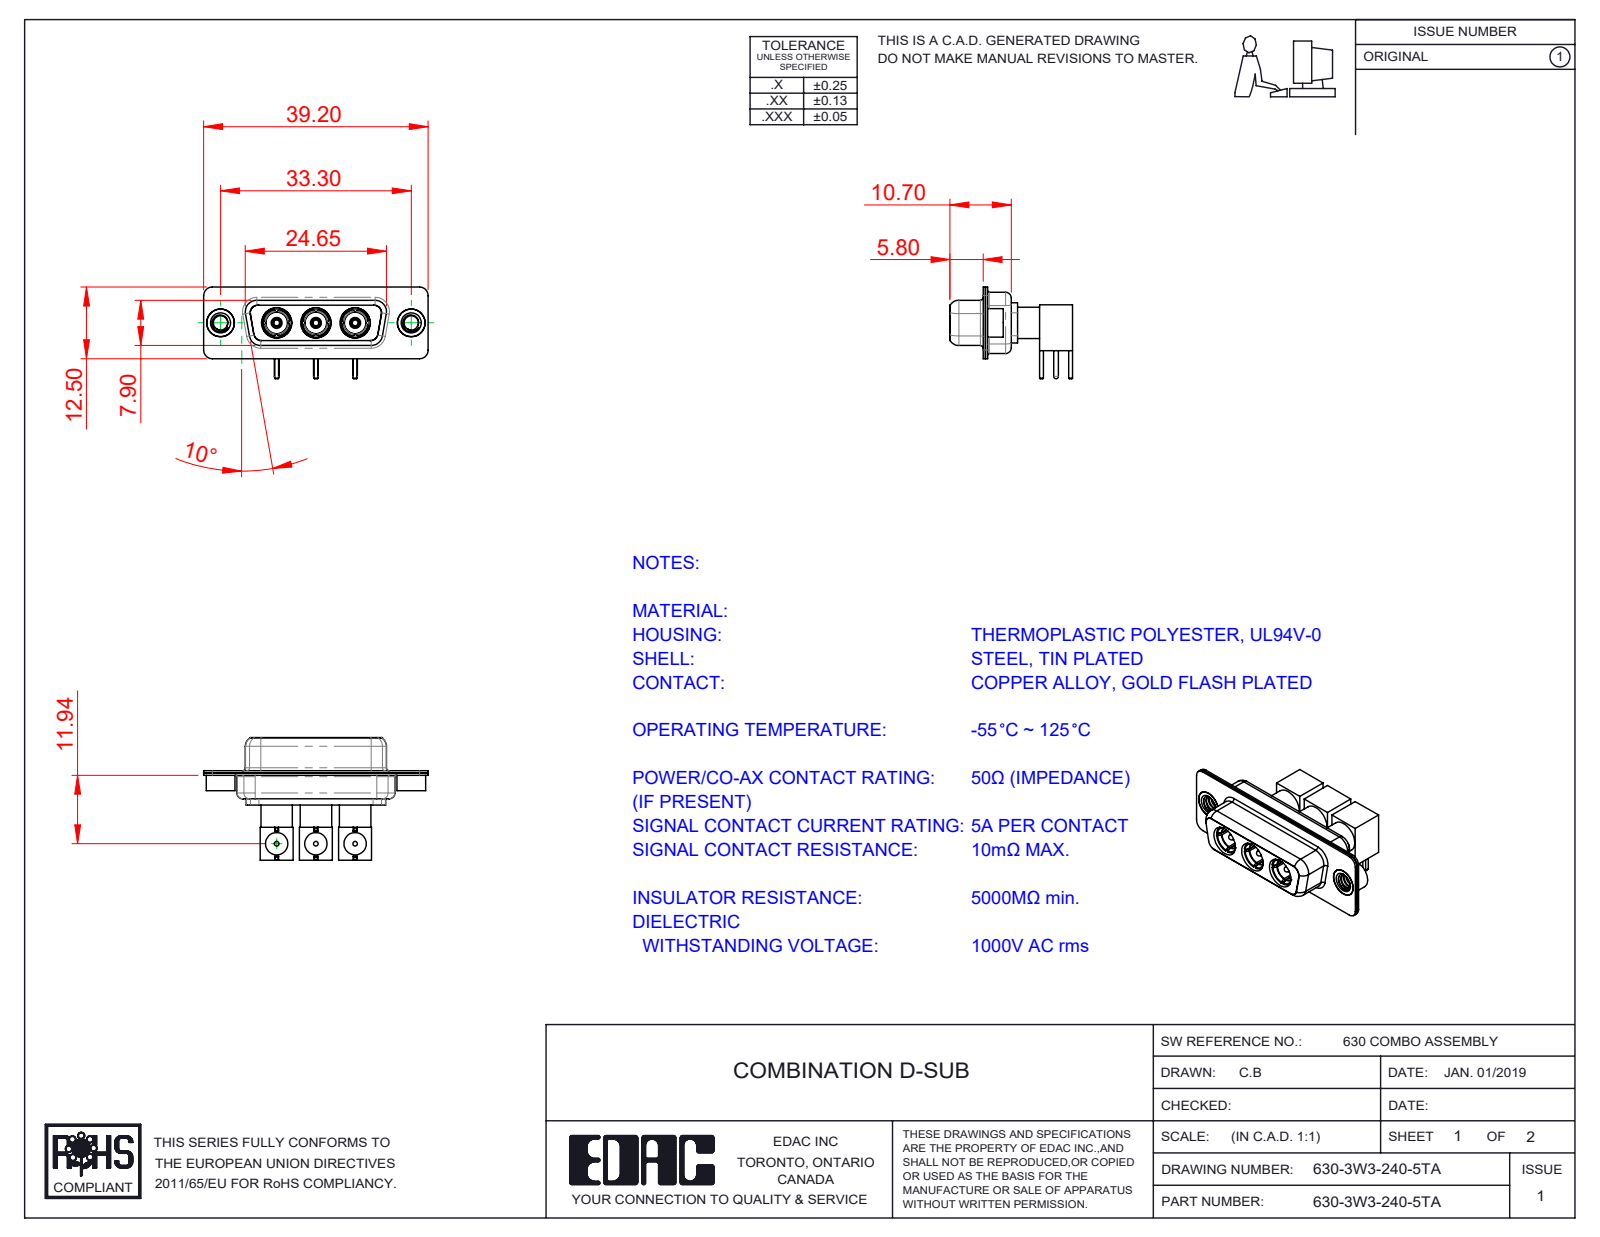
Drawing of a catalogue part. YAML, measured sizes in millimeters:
part_name: "630Combo Threaded Rivet_A; 630-3W3-240-5TA; RA Back Shell; Co-Ax Plug Assy_RA (+8 more)"
step_written_by: "SolidWorks 2020 (CONFIG_CONTROL_DESIGN)"
units: millimeters
bodies: {solids: 23, faces: 777, planar: 268, cylindrical: 330, other: 179}
overall_size: [39.2, 21.41, 16]
volume: 3133
surface_area: 7793
round_holes:
  - {diameter: 4.85, count: 5}
  - {diameter: 0.8, count: 3}
  - {diameter: 1.1, count: 3}
  - {diameter: 1.5, count: 3}
  - {diameter: 2.83, count: 3}
  - {diameter: 3.1, count: 3}
  - {diameter: 3.3, count: 3}
  - {diameter: 3.9, count: 3}
  - {diameter: 3.92, count: 3}
  - {diameter: 4.1, count: 3}
  - {diameter: 5.3, count: 3}
  - {diameter: 2.5, count: 2}
round_bosses_or_shafts:
  - {diameter: 5, count: 5}
  - {diameter: 5.5, count: 3}
  - {diameter: 5.2, count: 3}
  - {diameter: 4.75, count: 3}
  - {diameter: 4.15, count: 3}
  - {diameter: 4, count: 3}
  - {diameter: 3.76, count: 3}
  - {diameter: 3.75, count: 3}
partial_cylinders:
  - {radius: 1.5, count: 16}
  - {radius: 1.35, count: 12}
  - {radius: 2, count: 12}
  - {radius: 1.6, count: 8}
  - {radius: 0.25, count: 4}
  - {radius: 0.5, count: 4}
  - {radius: 0.6, count: 4}
  - {radius: 0.65, count: 4}
face_to_face_distances: [0.4, 1.8, 1.4, 0.45, 8.45, 0.8, 8.9, 1.85, 6.85, 6.2]
hole_center_spacings: [6.85, 9.8, 13.7, 16.65, 23.5, 33.3]
